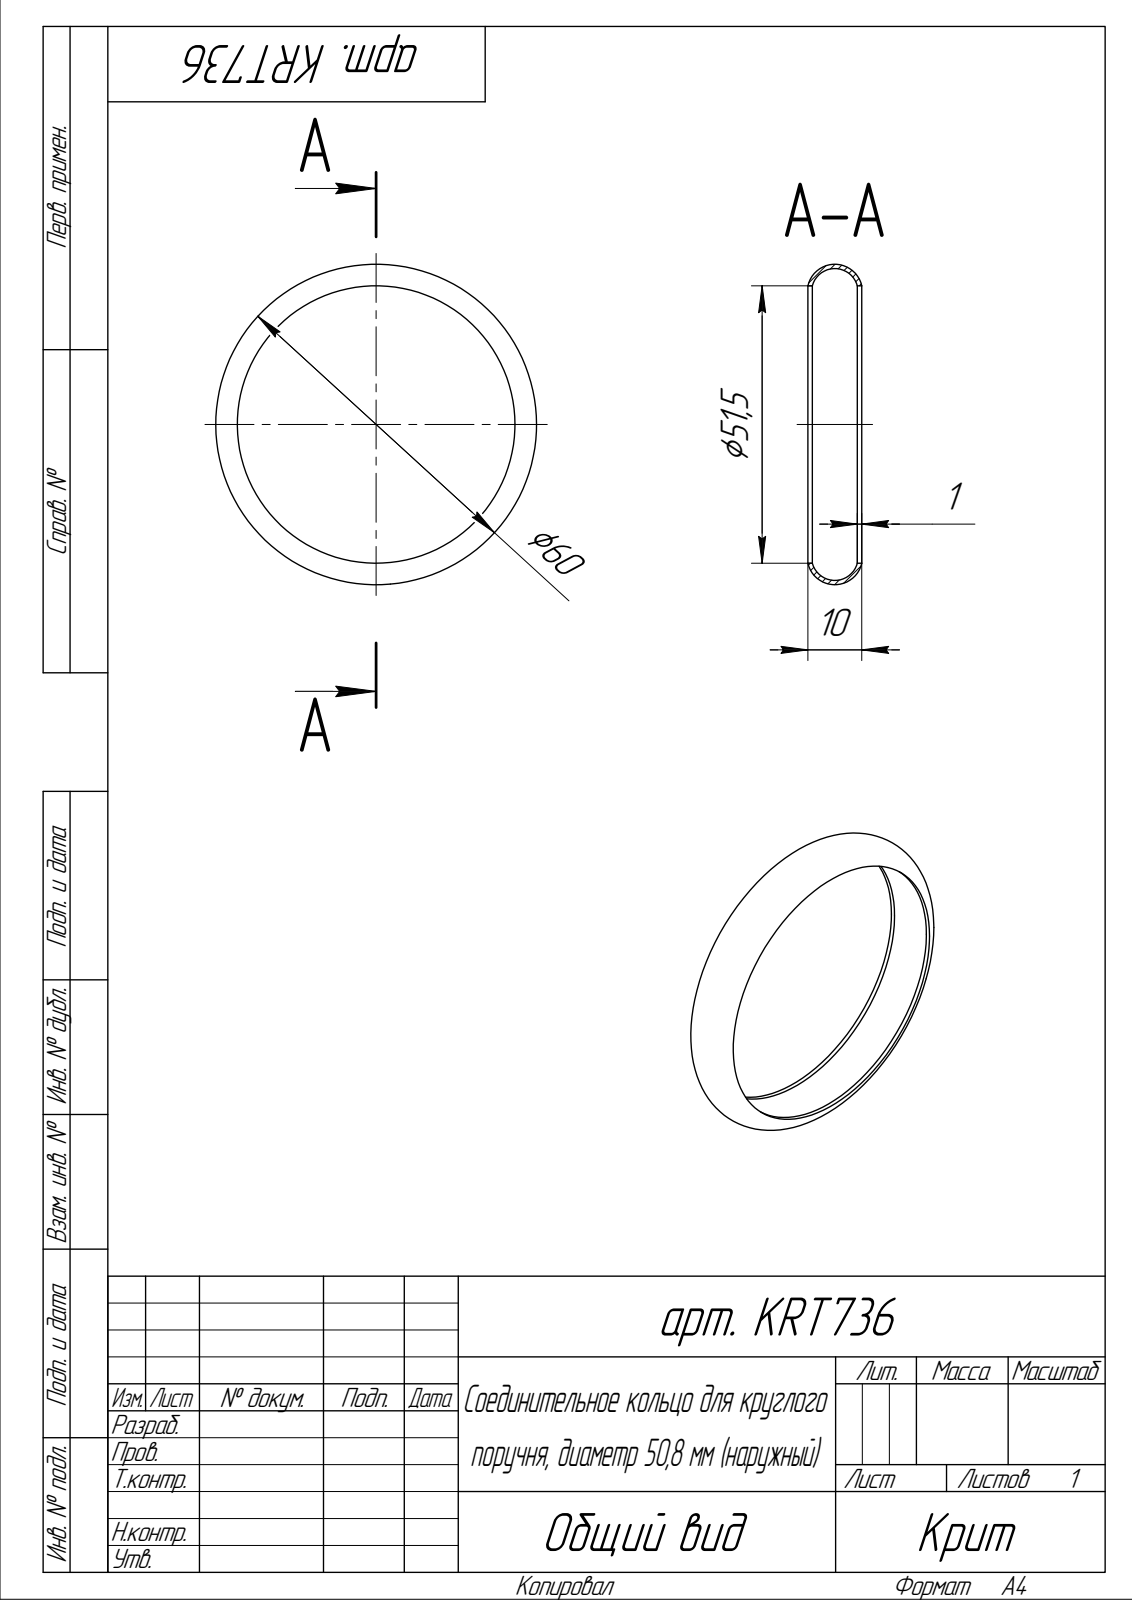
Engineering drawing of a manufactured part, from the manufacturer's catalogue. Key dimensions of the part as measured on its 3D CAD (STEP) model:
Part name (STEP PRODUCT): Деталь
STEP written by: ASCON Math Kernel (AUTOMOTIVE_DESIGN)
Units: millimetres
Bodies: 1 solid, 4 faces (0 planar, 2 cylindrical, 2 other)
Overall size (bounding box): 59.5 × 59.5 × 10
Volume: 1 775 mm³ · Surface area: 4 706 mm²
Round holes (diameter × count): ⌀51.5 ×1
